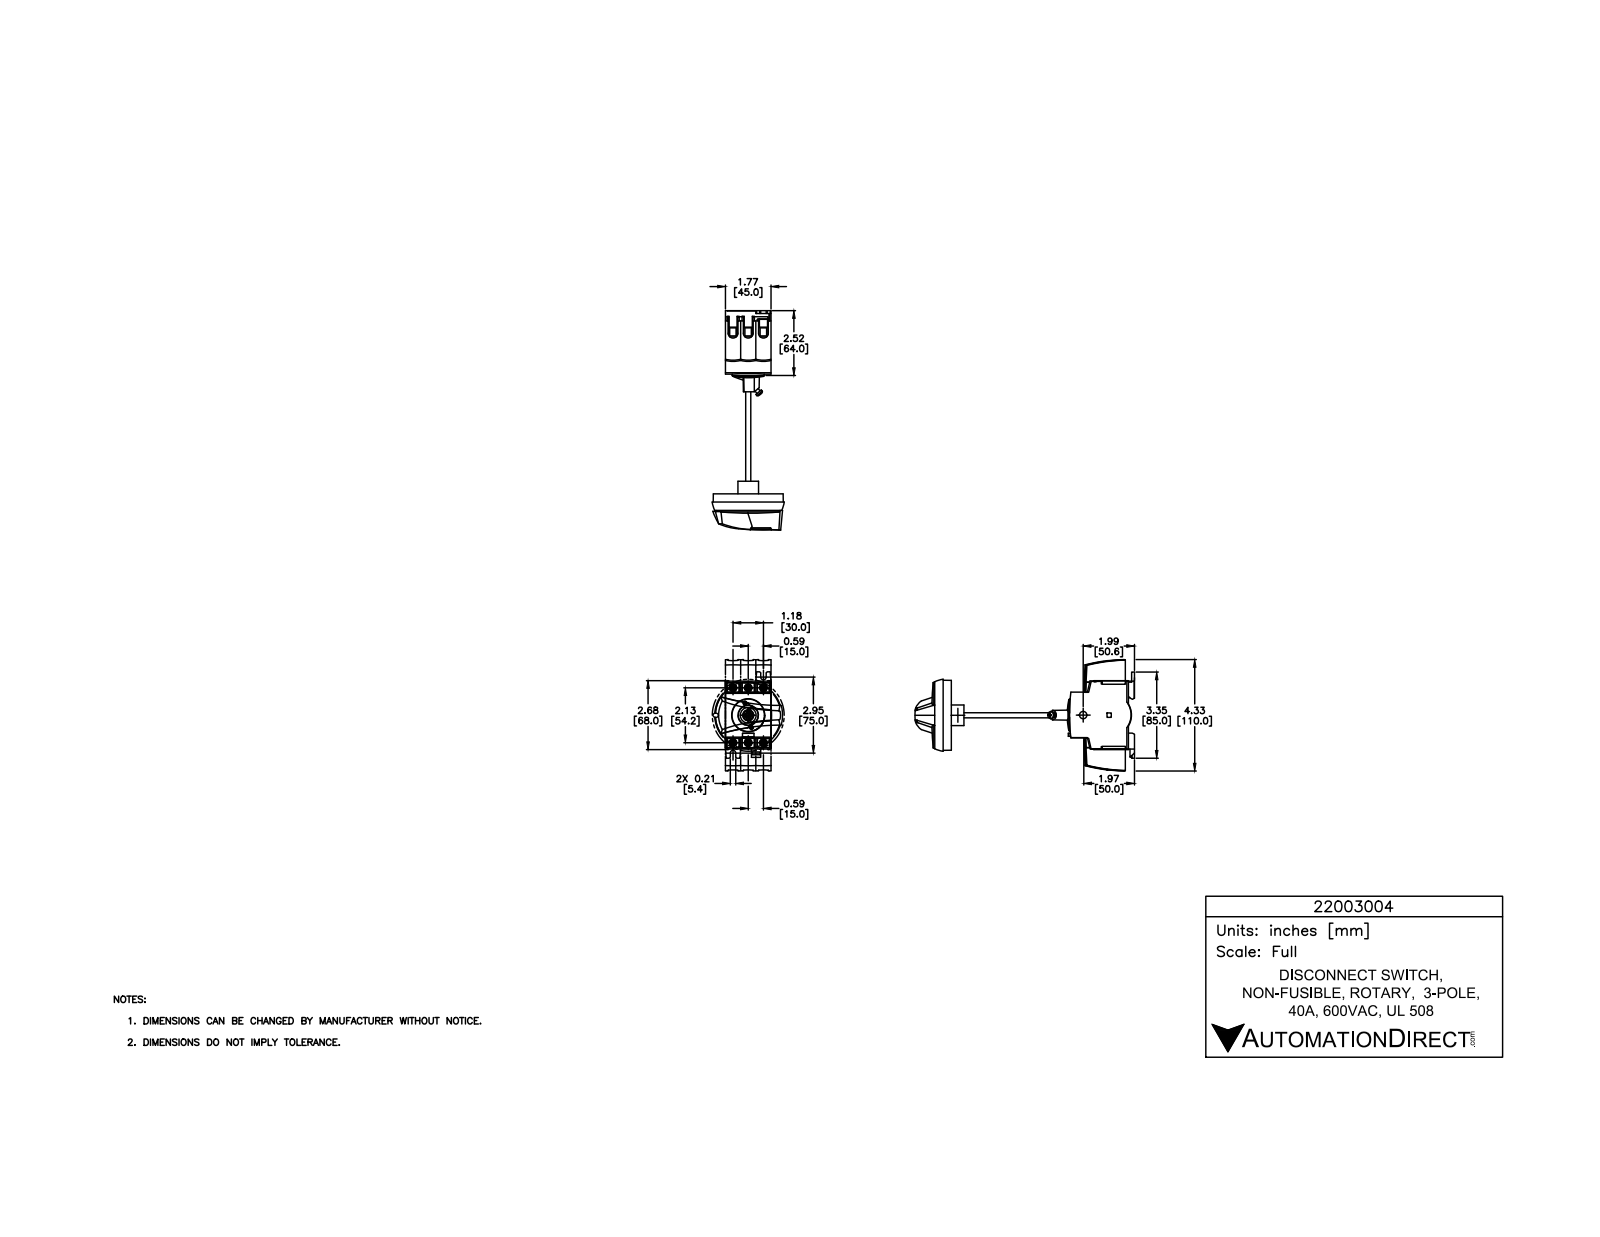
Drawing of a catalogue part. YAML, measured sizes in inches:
part_name: "22003004-UL"
step_written_by: "SolidWorks 2021 (CONFIG_CONTROL_DESIGN)"
units: inches
bodies: {solids: 1, faces: 463, planar: 389, cylindrical: 50, other: 24}
overall_size: [3.346, 2.571, 1.772]
volume: 9.498
surface_area: 40.23
round_holes:
  - {diameter: 0.26, count: 6}
  - {diameter: 0.283, count: 1}
  - {diameter: 1.244, count: 1}
partial_cylinders:
  - {radius: 0.012, count: 13}
  - {radius: 0.02, count: 5}
  - {radius: 0.165, count: 4}
  - {radius: 0.039, count: 3}
  - {radius: 0.106, count: 2}
  - {radius: 0.13, count: 1}
  - {radius: 0.354, count: 1}
  - {radius: 0.37, count: 1}
face_to_face_distances: [1.772, 0.433, 2.205, 2.157, 2.638, 2.28, 0.591, 2.591, 0.047, 0.386]
hole_center_spacings: [0.591, 1.219, 2.214, 2.134, 1.067, 1.181, 2.439]
